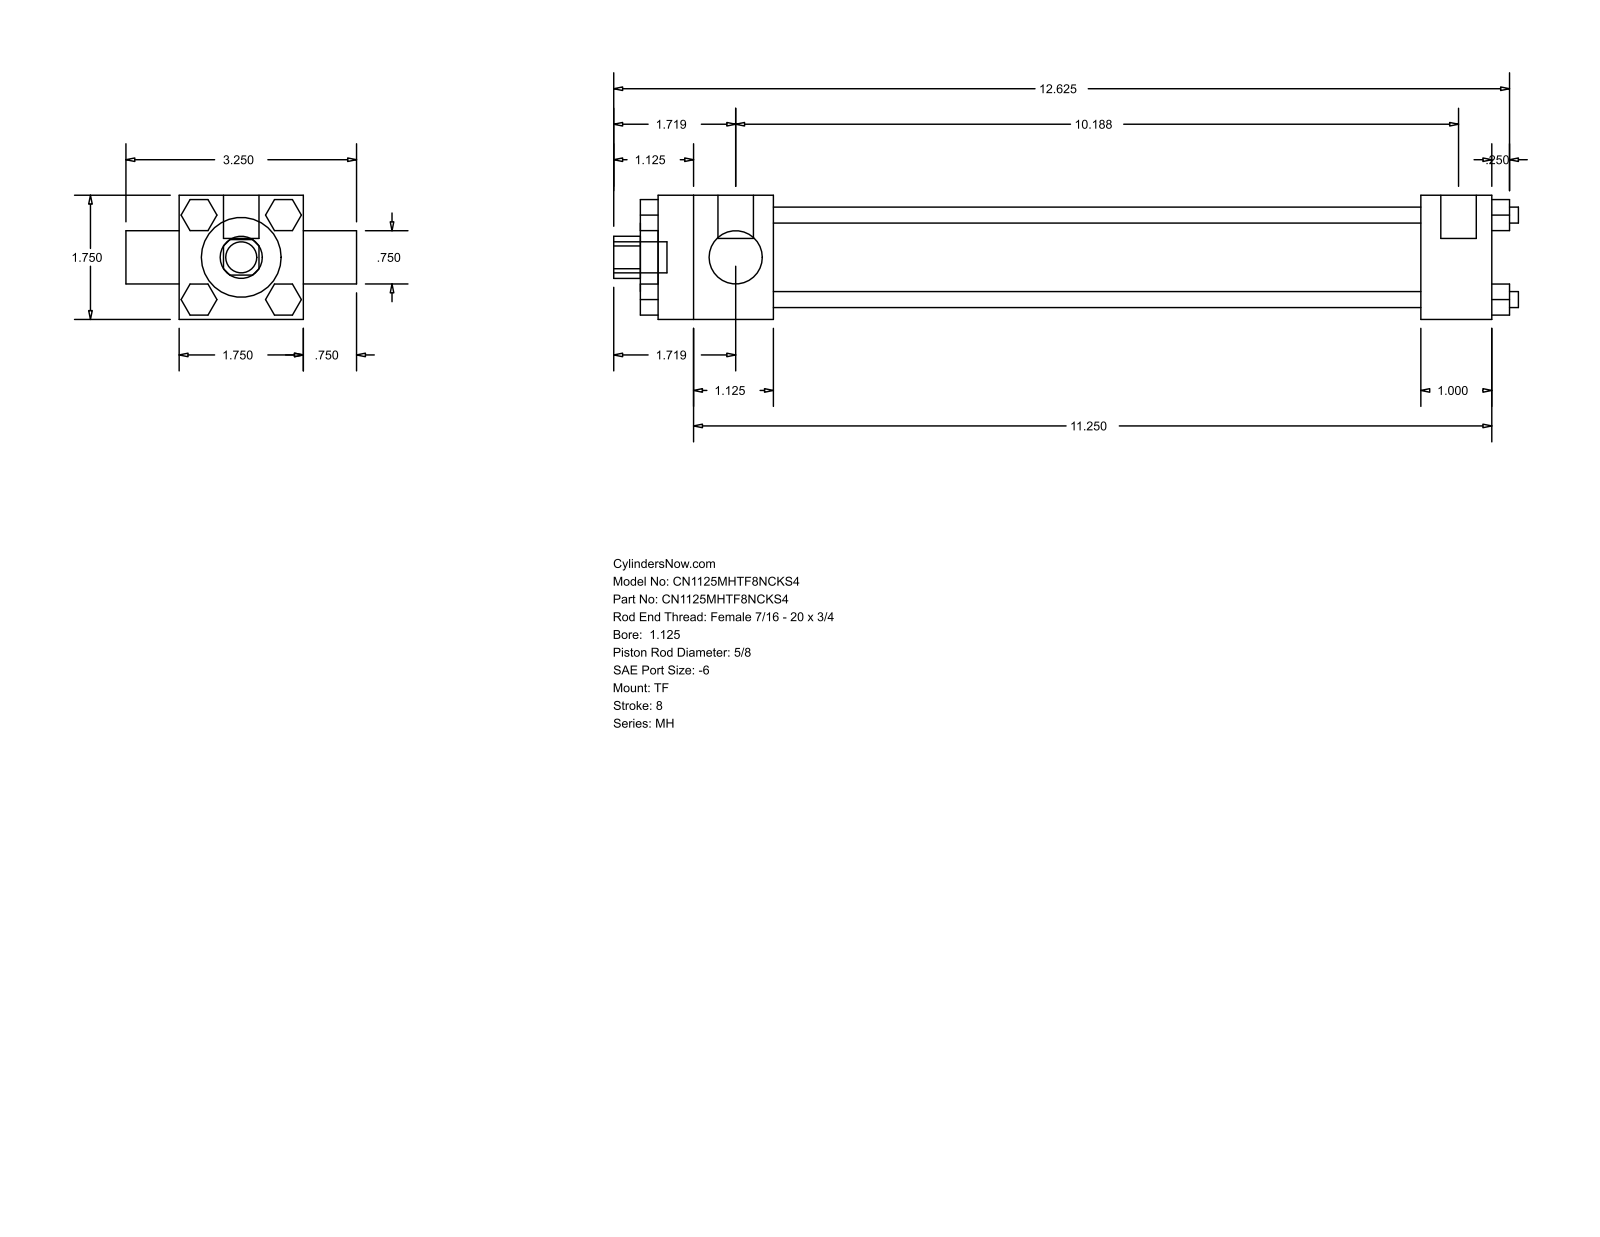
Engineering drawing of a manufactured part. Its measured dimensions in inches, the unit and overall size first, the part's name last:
Units: inches
Overall size (bounding box): 12.75 × 3.25 × 1.75
Round holes (diameter × count): ⌀0.625 ×1, ⌀0.75 ×1, ⌀1.125 ×1, ⌀1.375 ×1
Round bosses / shafts (diameter × count): ⌀0.225 ×4, ⌀0.219 ×3, ⌀0.5 ×2, ⌀0.437 ×1
Partial cylindrical surfaces — rounded edges, fillets, slot ends (radius × count): R0.297 ×1
Main face-to-face distances: 1.75, 0.437, 9.125, 10.125, 1, 1.625, 10.75, 11.75, 1.875, 0.25
Bodies: 0 solids, 120 faces (92 planar, 28 cylindrical, 0 other)
Part name (STEP PRODUCT): MH_TF__0112_0.625
STEP written by: GSSL Pune (CONFIG_CONTROL_DESIGN)
